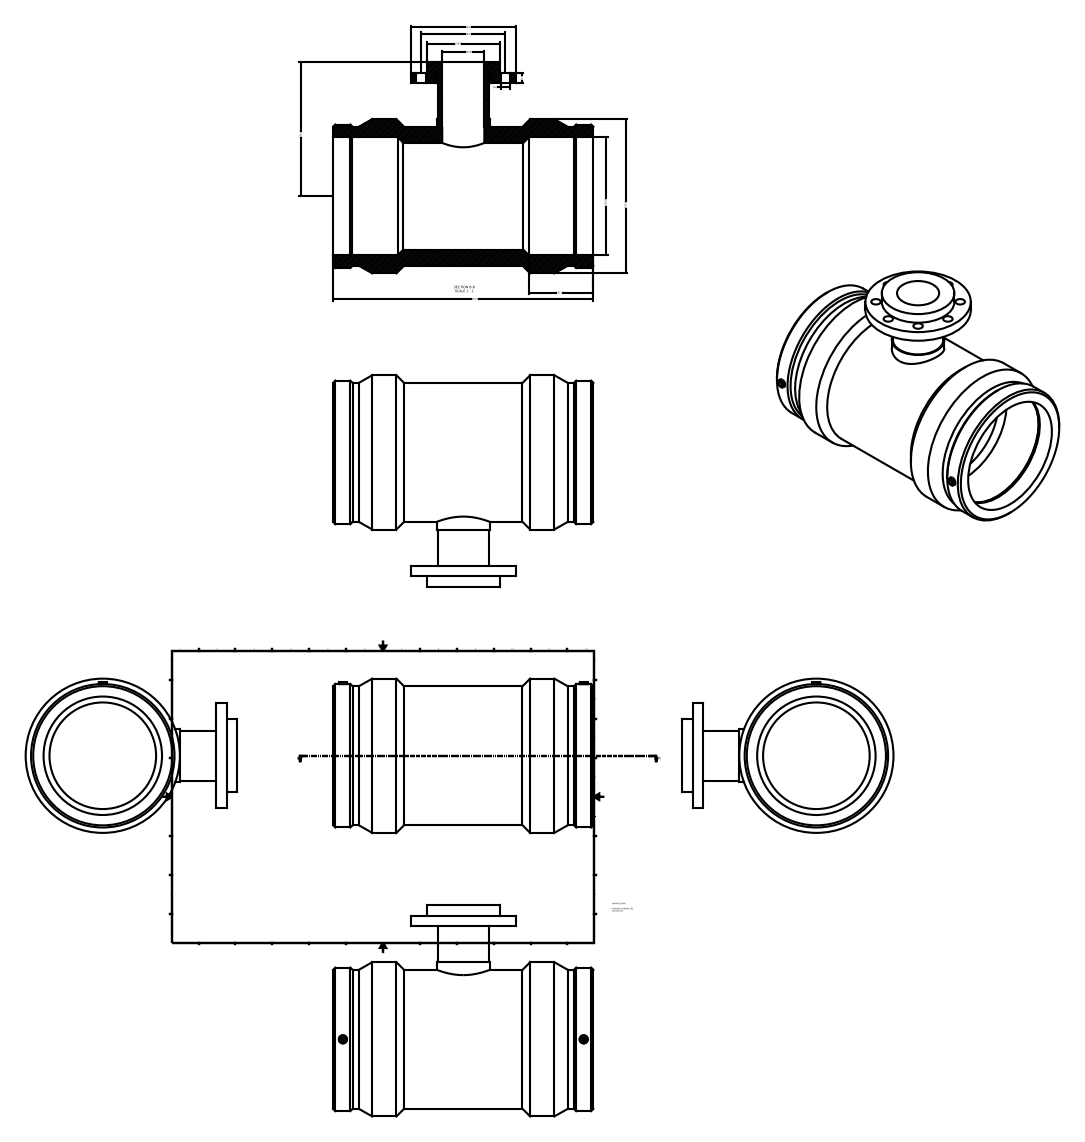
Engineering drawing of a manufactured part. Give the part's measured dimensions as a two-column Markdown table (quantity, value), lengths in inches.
| quantity | value |
| --- | --- |
| part name | 499404225080 |
| STEP written by | Autodesk Inventor 2015 (AUTOMOTIVE_DESIGN) |
| units | inches |
| bodies | 1 solid, 60 faces (14 planar, 30 cylindrical, 16 other) |
| overall size | 19.449 × 15.807 × 11.535 |
| volume | 719.5 in³ |
| surface area | 1 488 in² |
| round holes (diameter × count) | 0.709 × 8, 0.394 × 2, 3.15 × 1, 4.094 × 1, 7.972 × 1, 8.858 × 1 |
| round bosses / shafts (diameter × count) | 0.157 × 2, 11.535 × 1, 10.728 × 1, 10.406 × 1, 10.382 × 1, 7.874 × 1, 5.433 × 1, 3.937 × 1 |
| main face-to-face distances | 0.787, 19.449, 1.575, 1.419, 18.03, 4.272, 3.484, 2.697, 16.611, 0.551 |
| hole center spacings | 2.411, 3.15, 4.454, 5.82, 6.299, 18.008 |
